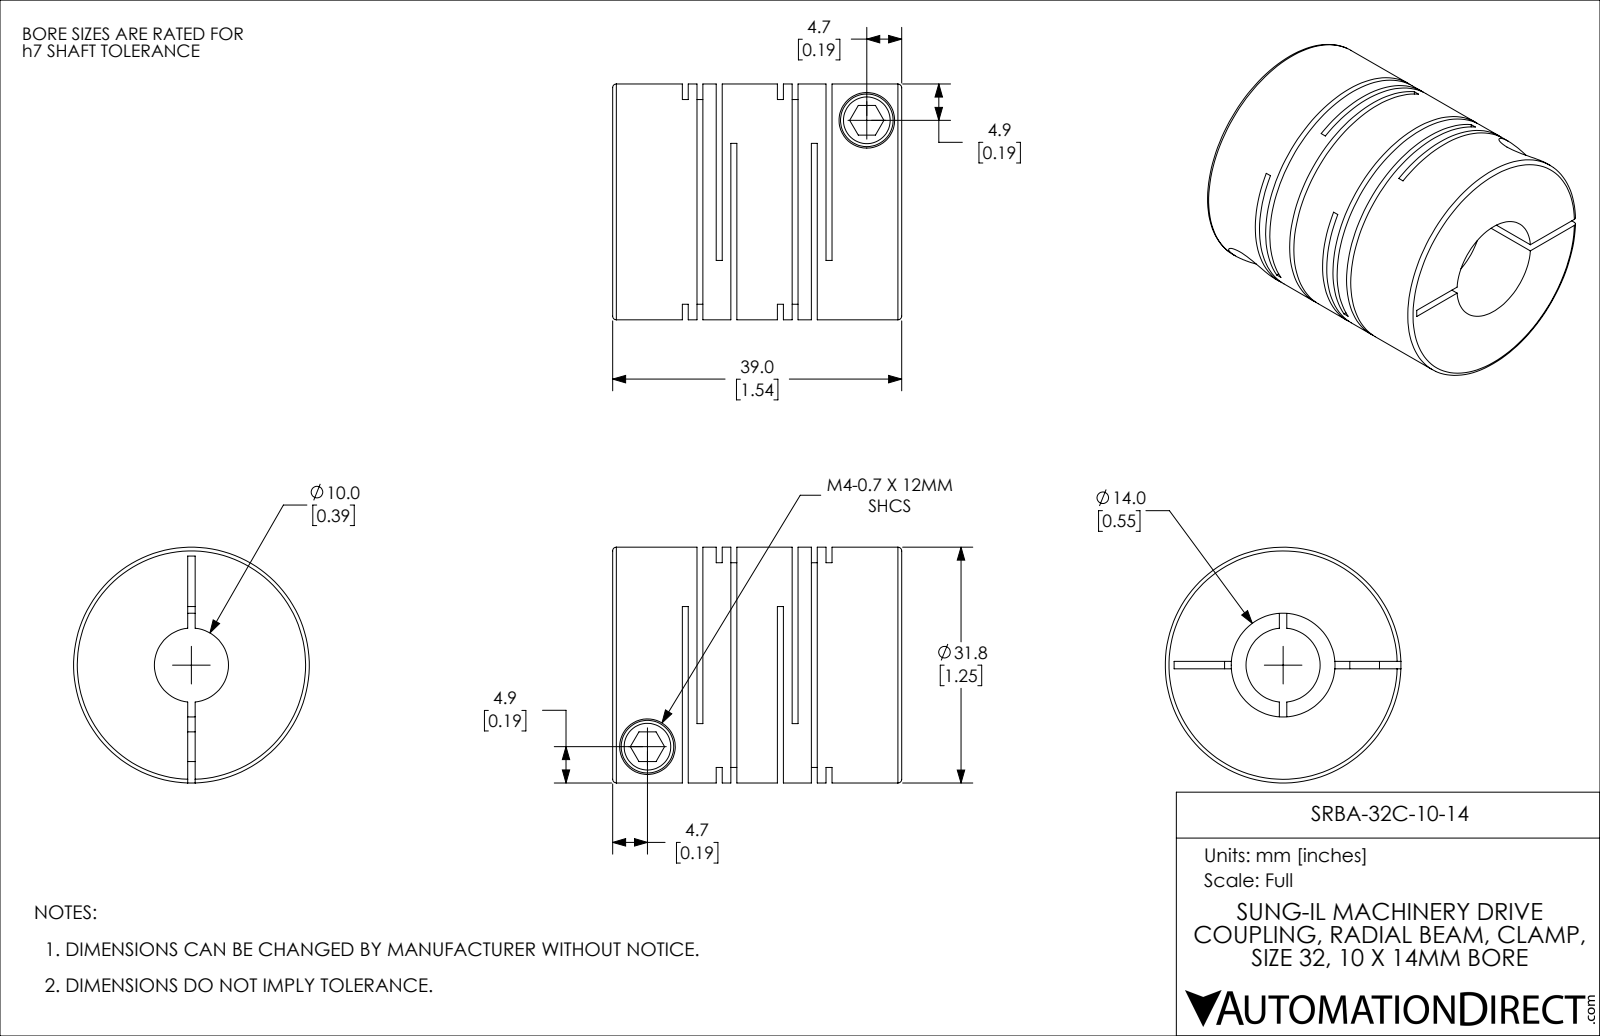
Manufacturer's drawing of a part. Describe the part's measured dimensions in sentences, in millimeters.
The part is named "SRBA-32C-10-14". Its 3-D file was written by "SolidWorks 2021 (CONFIG_CONTROL_DESIGN)". It is 1 solid with 114 faces: 60 planar, 42 cylindrical and 12 other. Overall it measures 39 by 31.8 by 31.8 millimeters. Its volume is 21 738 cubic millimeters and its surface area 15 226 square millimeters. Round holes: 2 of diameter 4, 2 of diameter 7.5, 1 of diameter 10, 1 of diameter 14. Round bosses or shafts: 2 of diameter 7.1, 1 of diameter 31.8. The main face-to-face distances are 0.8, 12.84, 1.98, 4.58, 12.04, 1.18, 10.86, 3.78, 8.26, 2.6.
